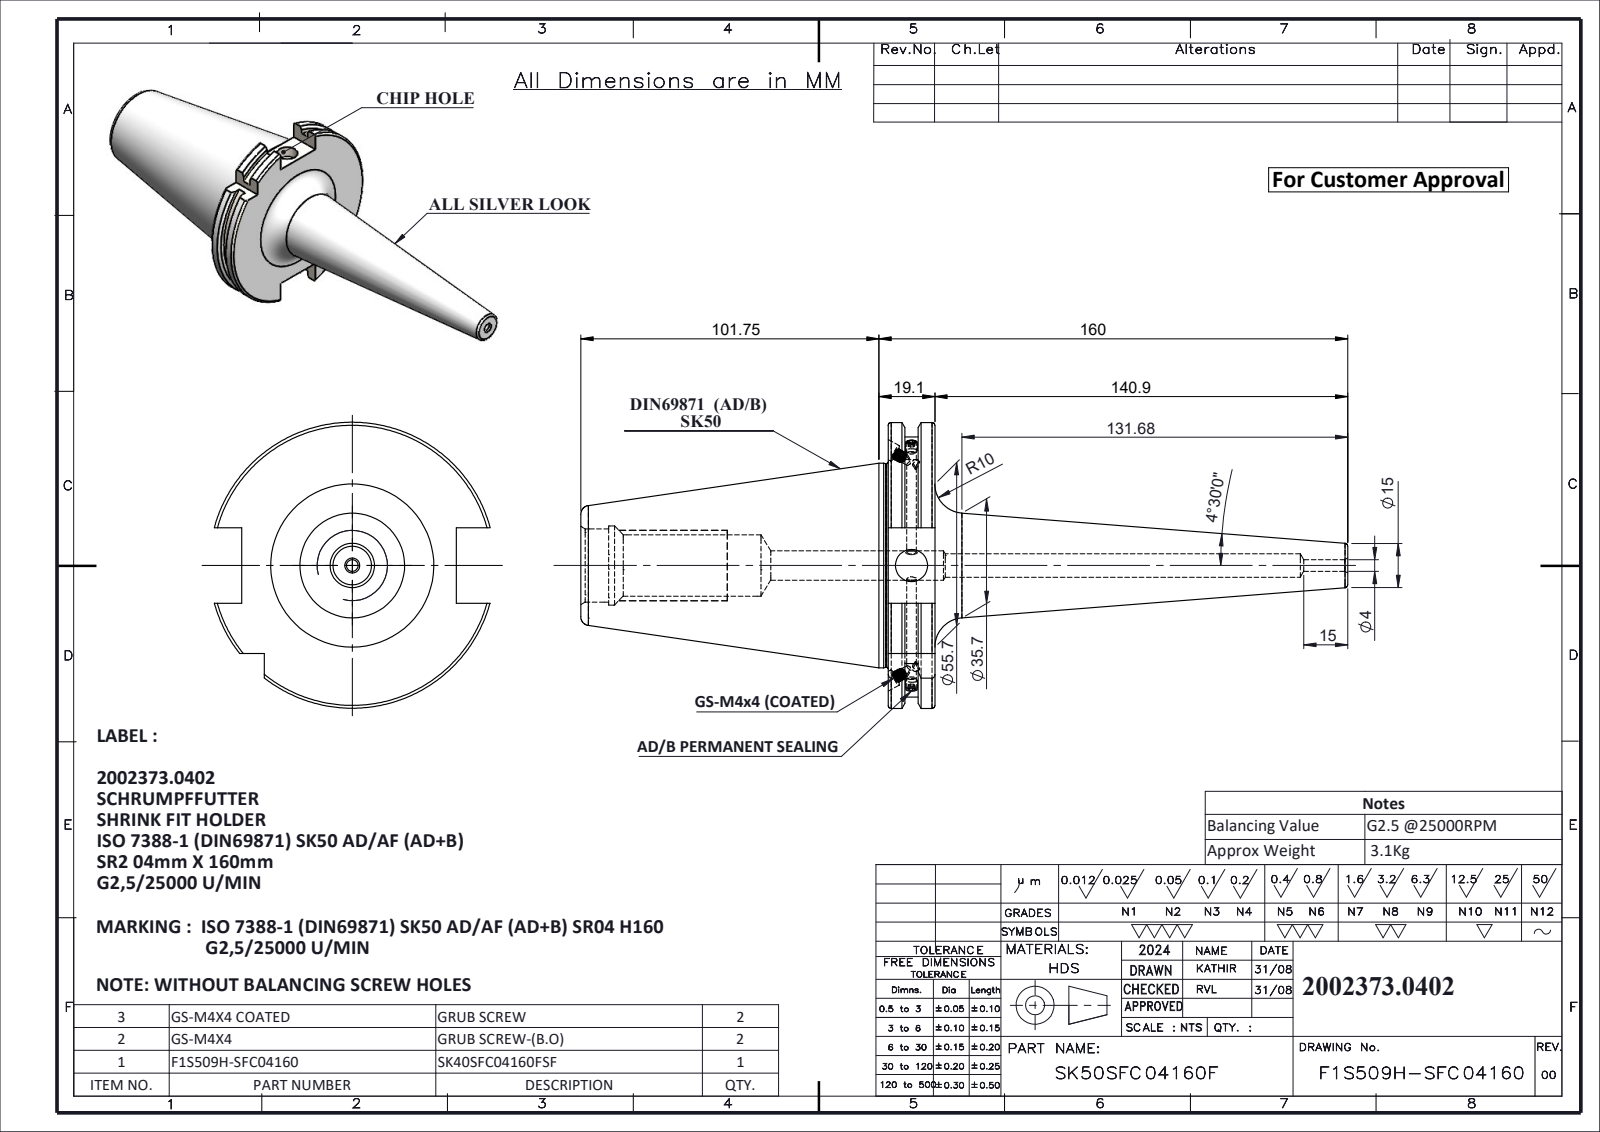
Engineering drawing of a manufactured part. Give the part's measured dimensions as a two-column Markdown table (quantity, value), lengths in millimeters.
| quantity | value |
| --- | --- |
| part name | F1S509H-SFC04160; SK50SFC04160FWW; GS-M4X4_DIN 913 - M4 x 4-N; GS-M4X4-COATING_DIN 913 - M4 x 4-N |
| STEP written by | SolidWorks 2024 (CONFIG_CONTROL_DESIGN) |
| units | millimeters |
| bodies | 5 solids, 250 faces (61 planar, 73 cylindrical, 116 other) |
| overall size | 261.75 × 97.5 × 94.05 |
| volume | 409 056 mm³ |
| surface area | 57 402 mm² |
| round holes (diameter × count) | 3.2 × 2, 6 × 2, 3.3 × 1, 3.99 × 1, 8 × 1, 10 × 1, 11 × 1, 21 × 1, 25 × 1, 27 × 1 |
| round bosses / shafts (diameter × count) | 4 × 4, 2.9 × 2, 69.85 × 1, 69.45 × 1 |
| partial cylindrical surfaces (radius × count) | 44.9 × 1, 48.75 × 1 |
| main face-to-face distances | 15.9, 5.65, 10.25, 10.14, 4.49, 5.76, 104.95, 110.6, 115.09, 120.85 |
